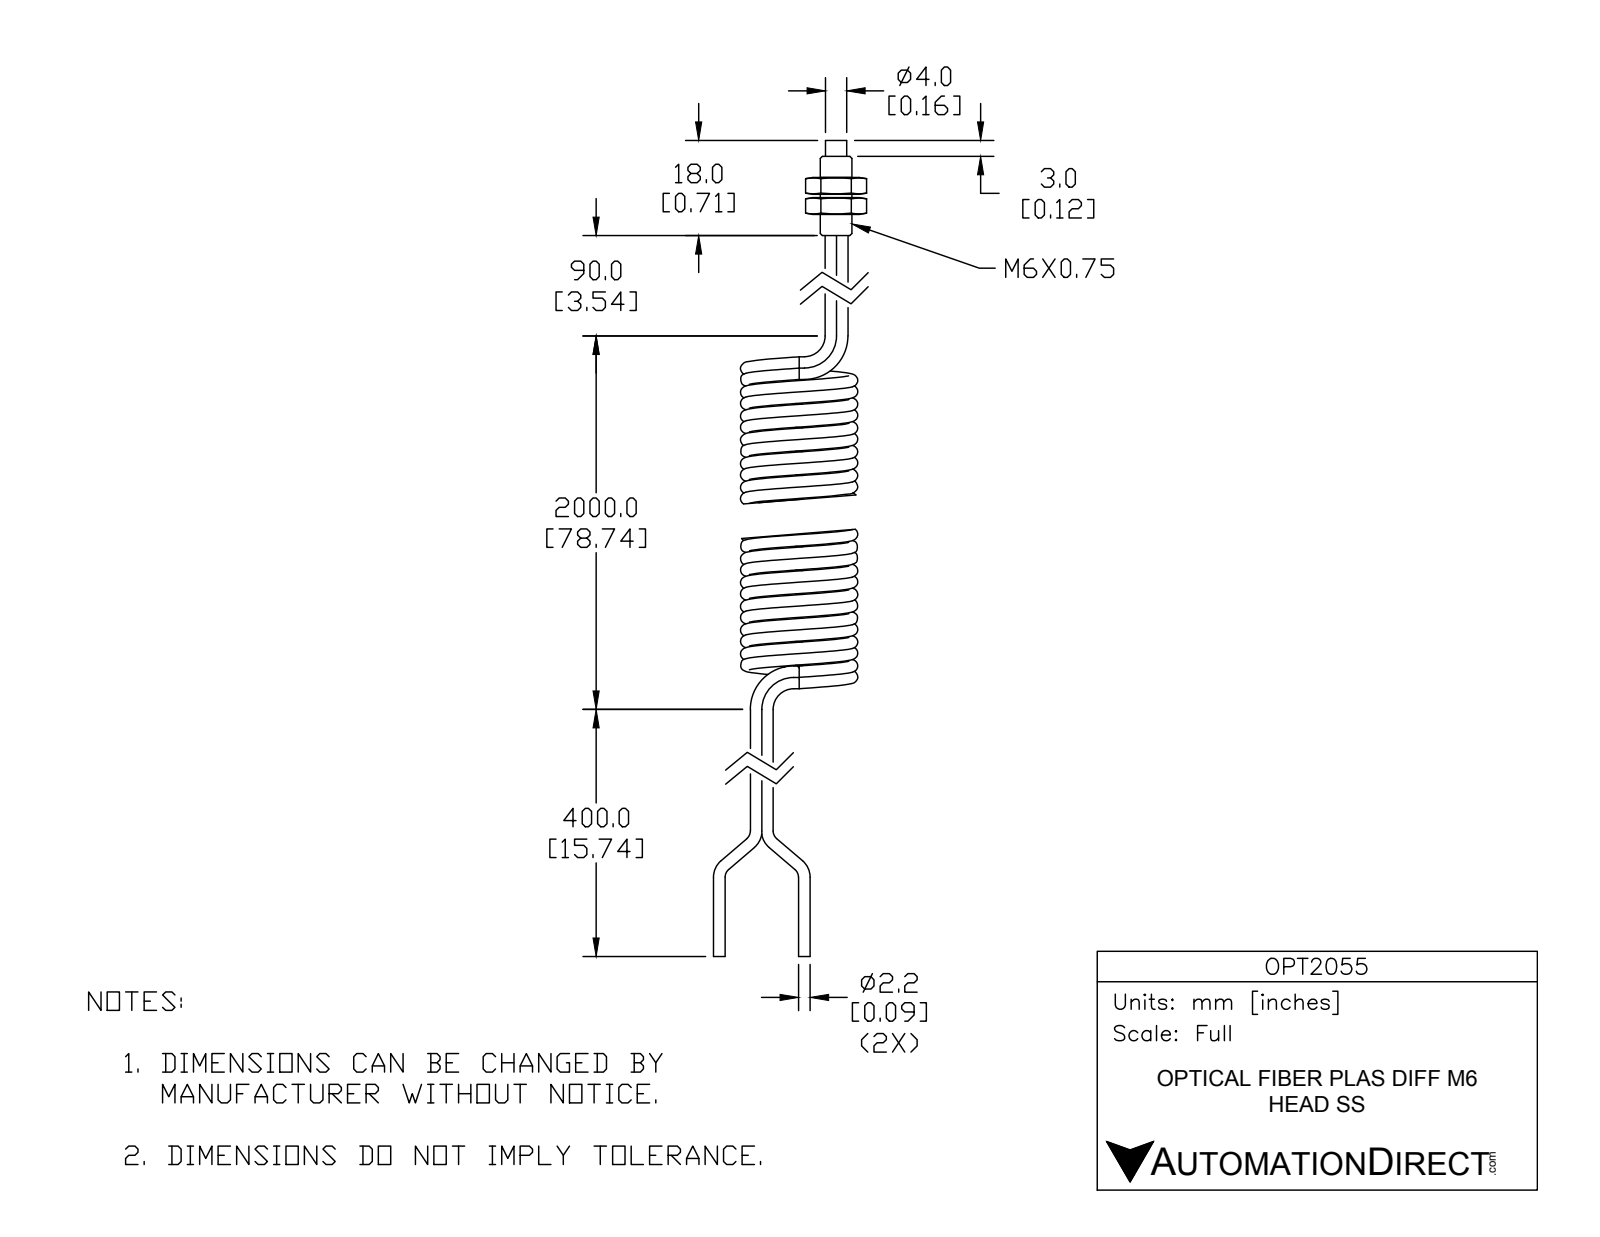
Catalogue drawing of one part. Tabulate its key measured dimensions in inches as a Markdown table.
| quantity | value |
| --- | --- |
| part name | OPT2055 |
| STEP written by | SolidWorks 2014 (AUTOMOTIVE_DESIGN) |
| units | inches |
| bodies | 5 solids, 117 faces (38 planar, 47 cylindrical, 32 other) |
| overall size | 6.078 × 1.141 × 1.028 |
| volume | 0.429 in³ |
| surface area | 16.92 in² |
| round bosses / shafts (diameter × count) | 0.087 × 12, 0.236 × 1, 0.157 × 1 |
| main face-to-face distances | 0.394, 0.255, 0.126, 0.15, 0.276, 0.024, 0.157, 0.283, 0.307, 0.433 |
